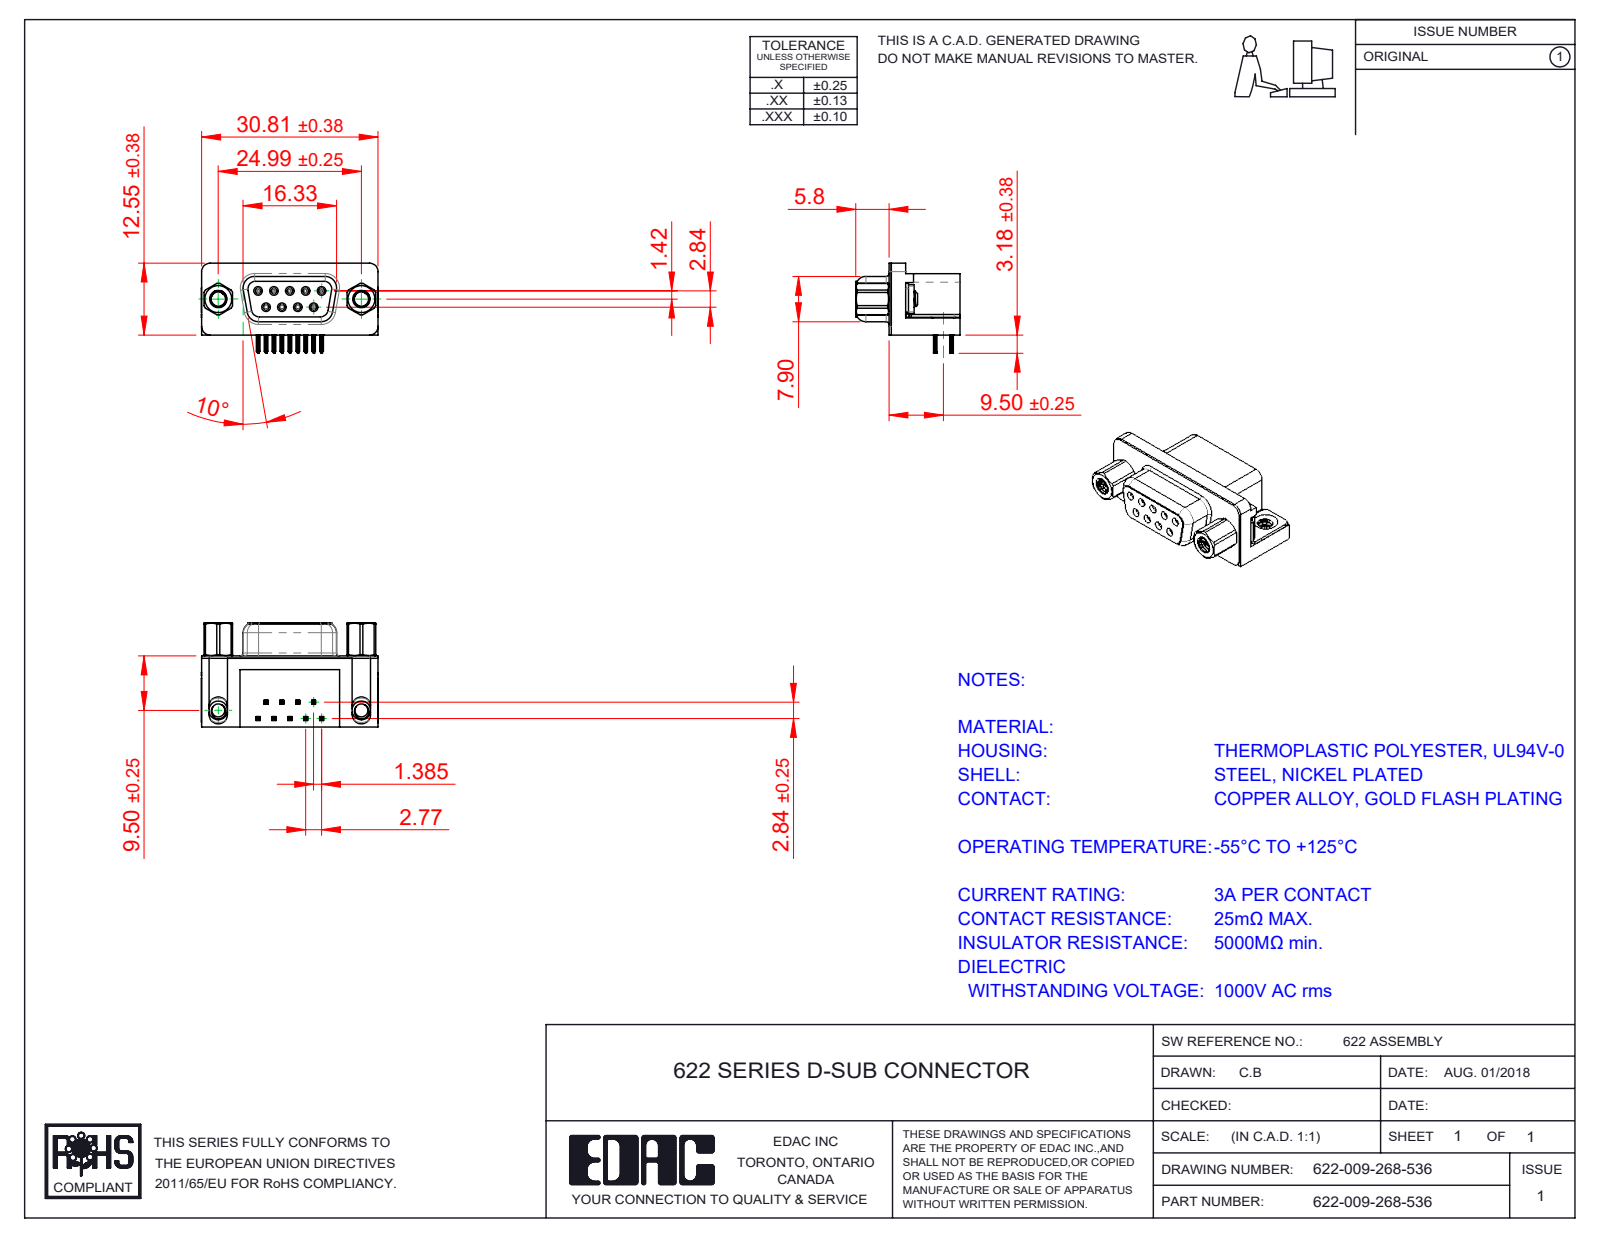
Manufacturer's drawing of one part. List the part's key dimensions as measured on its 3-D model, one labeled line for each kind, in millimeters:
Part name (STEP PRODUCT): 622 Housing_9 Socket; 622-009-268-536; 622 Contact Top; 622 M3 Threaded Rivet (+3 more)
STEP written by: SolidWorks 2016 (CONFIG_CONTROL_DESIGN)
Units: millimetres
Bodies: 15 solids, 1612 faces (716 planar, 428 cylindrical, 468 other)
Overall size (bounding box): 30.89 × 18.2 × 16.25
Volume: 3 720 mm³ · Surface area: 5 082 mm²
Round holes (diameter × count): ⌀0.8 ×9, ⌀0.9 ×9, ⌀2.5 ×2, ⌀4 ×2, ⌀4.8 ×2, ⌀5 ×2
Round bosses / shafts (diameter × count): ⌀1.2 ×9, ⌀4.9 ×2, ⌀4.75 ×2, ⌀3.9 ×2
Partial cylindrical surfaces — rounded edges, fillets, slot ends (radius × count): R0.1 ×72, R0.15 ×36, R0.35 ×18, R1 ×18, R0.5 ×10, R0.34 ×9, R0.25 ×8, R1.35 ×8
Main face-to-face distances: 0.4, 12, 12.4, 0.35, 2.9, 2.5, 6.2, 10.34, 0.5, 9.5
Hole centre spacings: 3.16, 2.77, 5.54, 5.03, 5.04, 8.31, 7.48, 7.49
